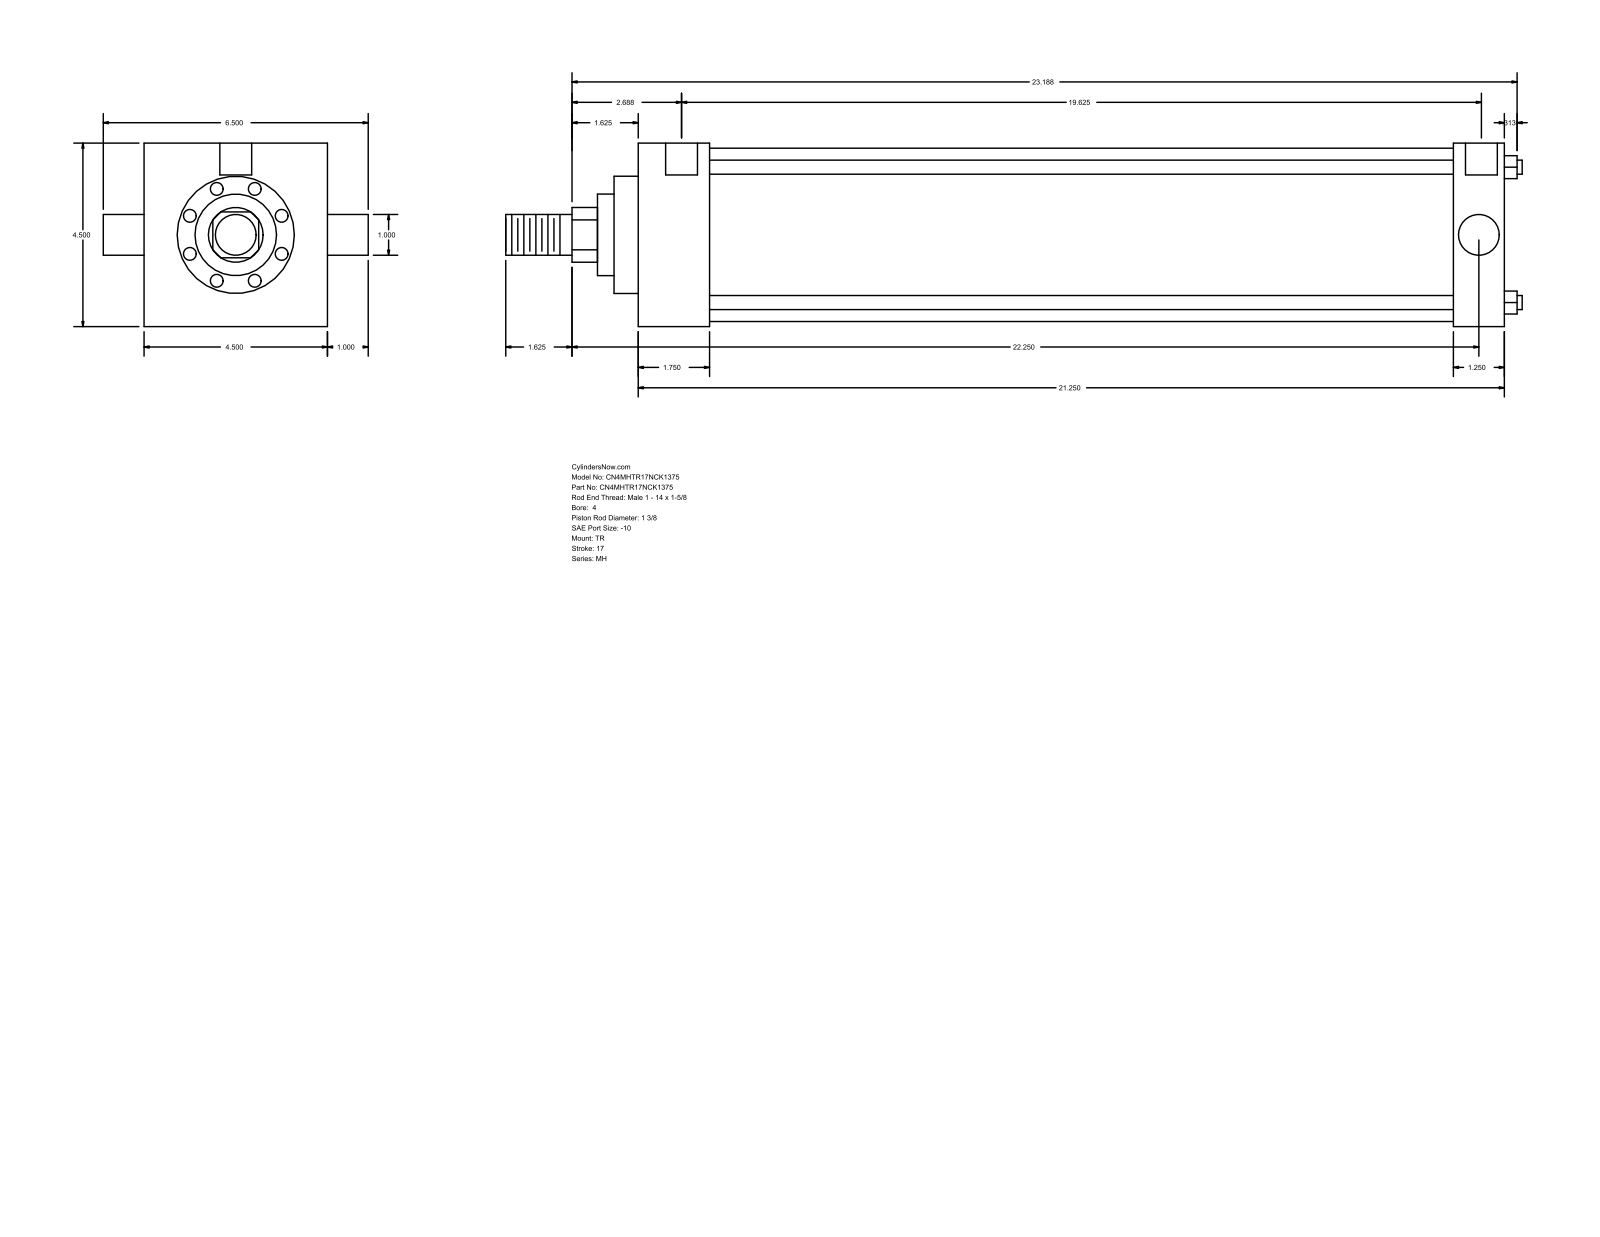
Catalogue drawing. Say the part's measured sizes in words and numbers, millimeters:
The part is named "MH_TR__0400_1.375". Its 3-D file was written by "GSSL Pune (CONFIG_CONTROL_DESIGN)". It is 0 solids with 86 faces: 61 planar, 25 cylindrical and 0 other. Overall it measures 633.41 by 165.1 by 114.3 millimeters. Round holes: 3 of diameter 8.73, 2 of diameter 19.84. Round bosses or shafts: 4 of diameter 8.76, 2 of diameter 25.4, 1 of diameter 107.95, 1 of diameter 73.03, 1 of diameter 50.8, 1 of diameter 34.92. Partial cylindrical surfaces (rounded edges, fillets, slot ends): 1 of radius 17.06. The main face-to-face distances are 114.3, 539.75, 44.45, 495.3, 508, 463.55, 31.75, 15.08, 59.53, 523.08. The hole center spacings are 1.59, 500.07, 498.48, 501.66.
